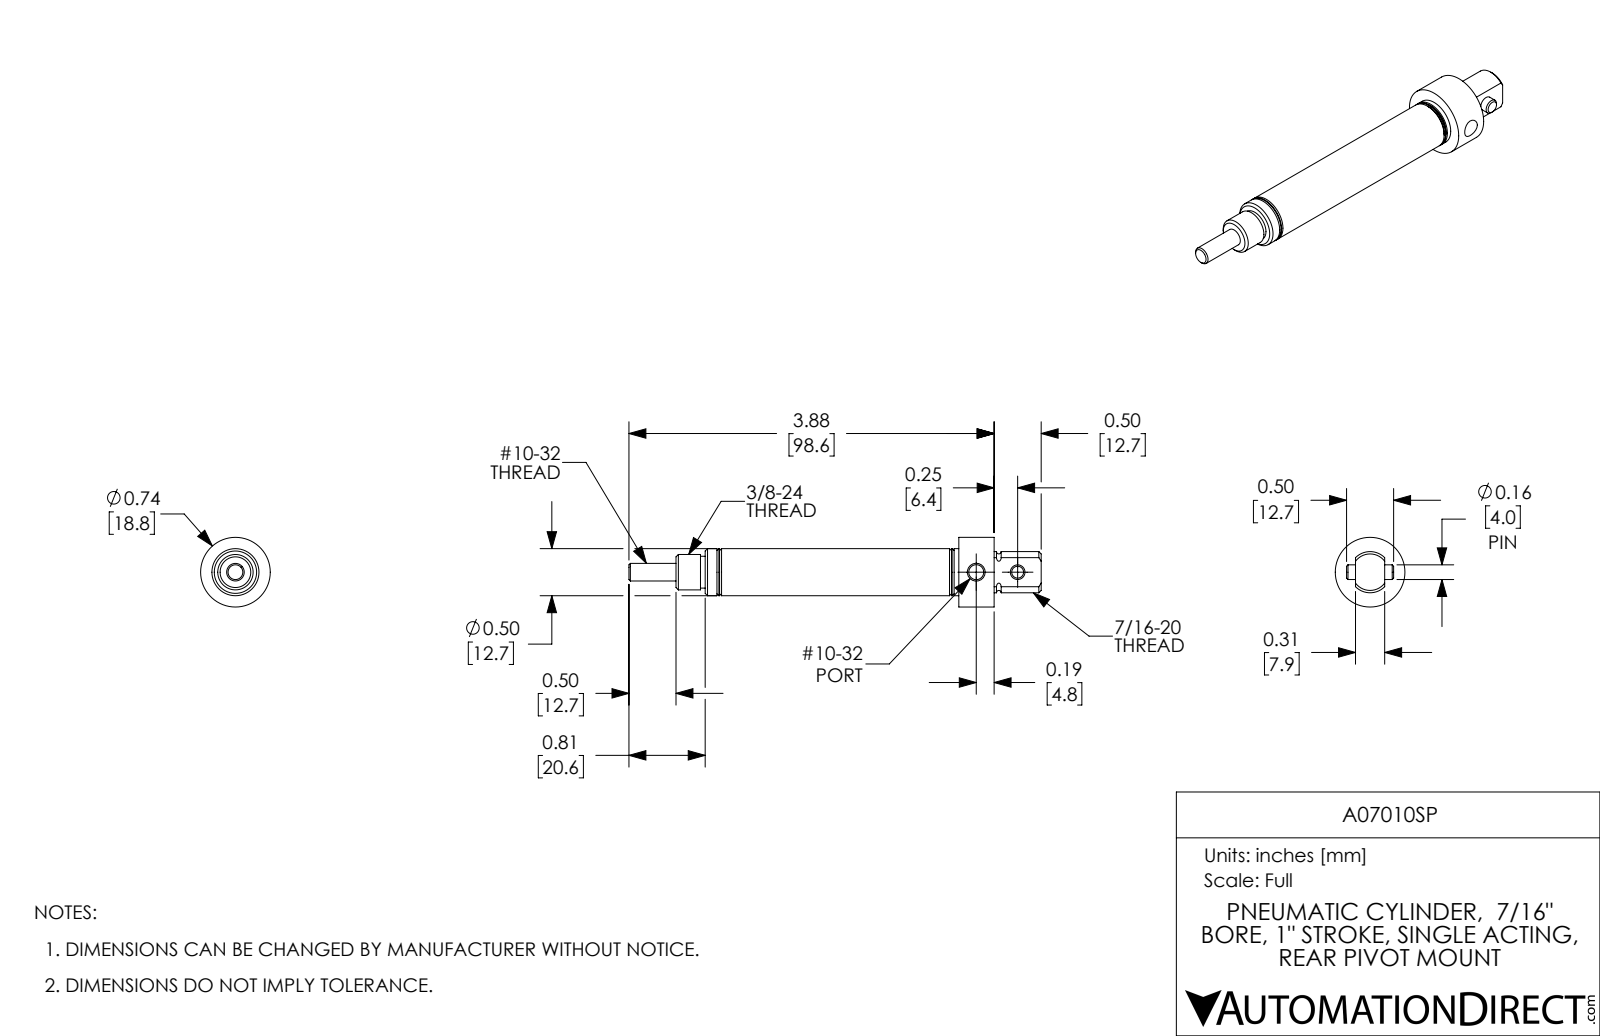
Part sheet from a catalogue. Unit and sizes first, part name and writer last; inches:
Units: inches
Overall size (bounding box): 4.38 × 0.74 × 0.74
Round holes (diameter × count): ⌀0.156 ×1, ⌀0.159 ×1, ⌀0.187 ×1, ⌀0.19 ×1
Round bosses / shafts (diameter × count): ⌀0.74 ×1, ⌀0.5 ×1, ⌀0.437 ×1, ⌀0.376 ×1, ⌀0.338 ×1
Main face-to-face distances: 0.785, 0.5, 0.375, 0.41, 1.285, 2.285, 1.785, 0.31, 0.91, 1.91
Hole centre spacings: 0.44
Volume: 0.664 in³ · Surface area: 13.27 in²
Bodies: 3 solids, 82 faces (20 planar, 36 cylindrical, 26 other)
Part name (STEP PRODUCT): A07010SP; A07010SP-Rod; A07010SP-Pin; A07010SP-MainBody
STEP written by: SolidWorks 2017 (AUTOMOTIVE_DESIGN)
